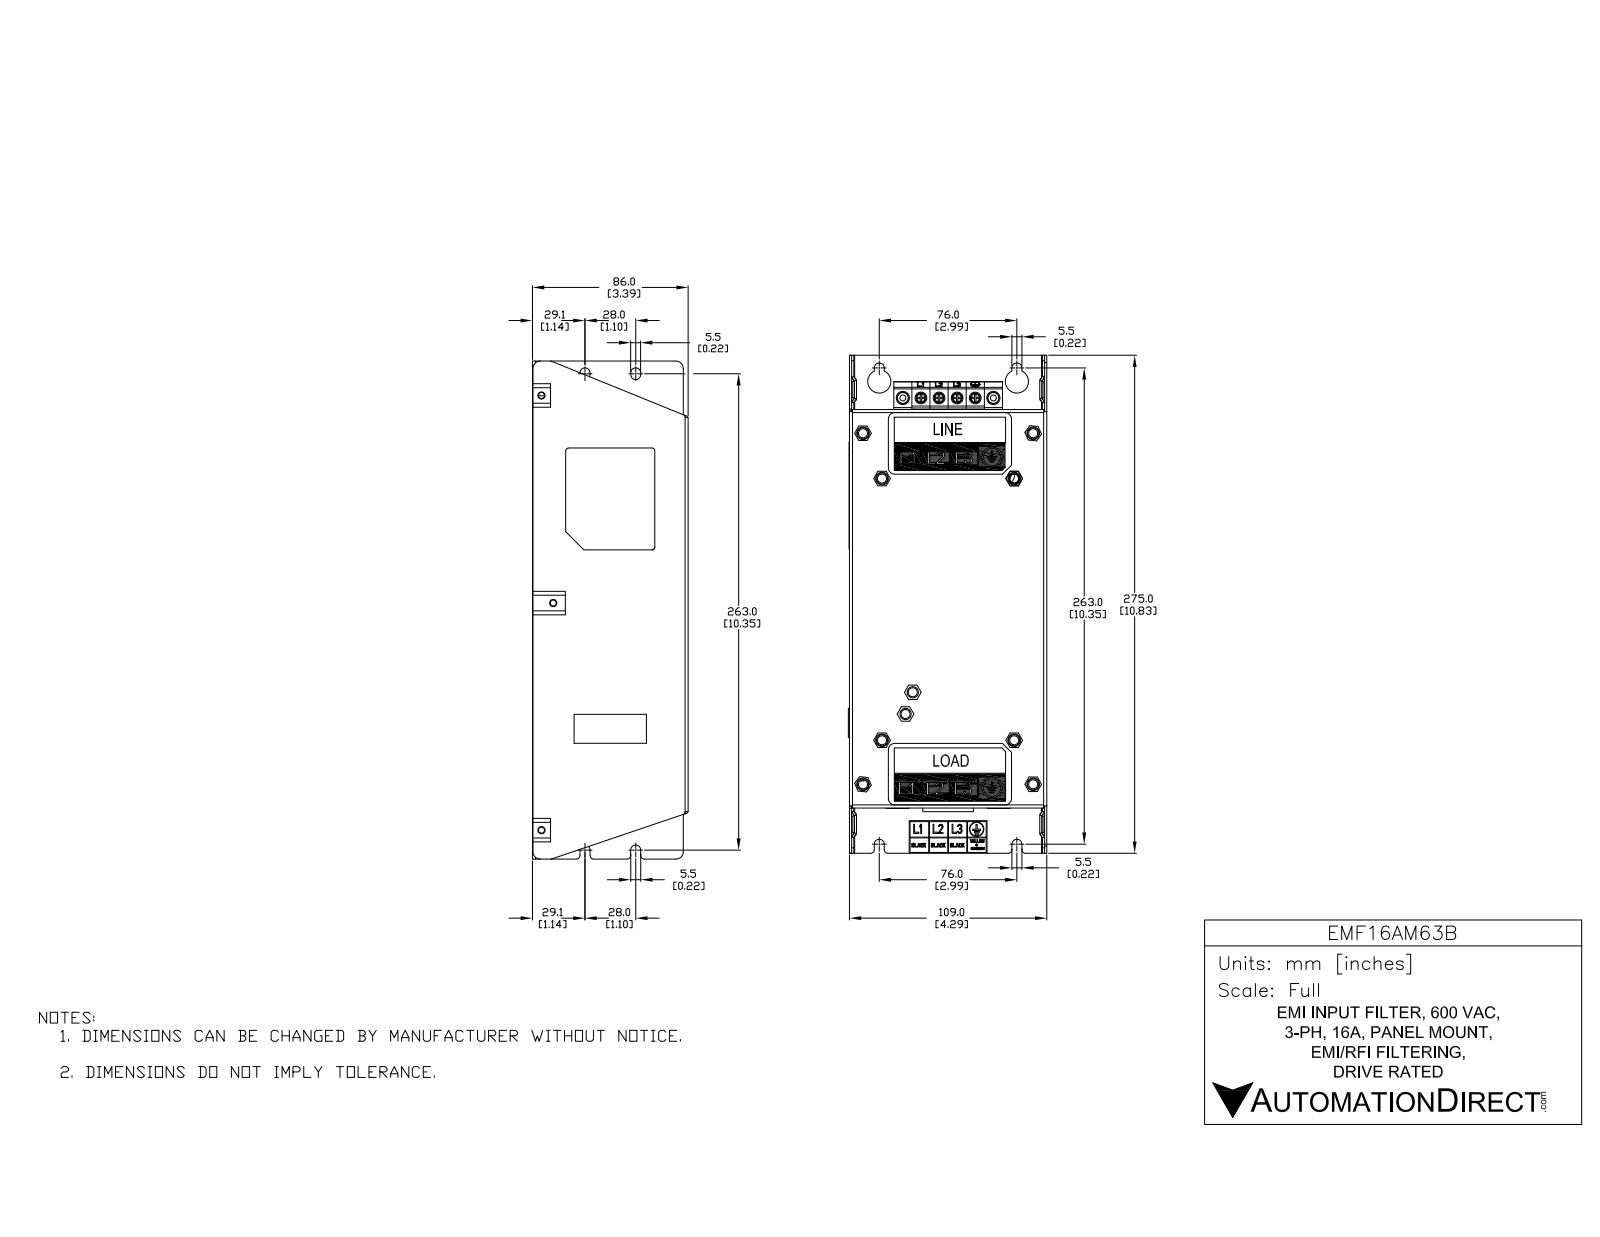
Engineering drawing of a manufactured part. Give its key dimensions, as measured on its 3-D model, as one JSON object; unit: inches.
{"part_name": "EMI B frame PRT0109 FROM wo surf 3 Coord COMPLETE E4 fXT Mod 1 r1", "step_written_by": "SolidWorks 2017 (AUTOMOTIVE_DESIGN)", "units": "inches", "bodies": {"solids": 15, "faces": 3208, "planar": 2058, "cylindrical": 618, "other": 532}, "overall_size": [10.827, 4.291, 3.39], "volume_in3": 10.93, "surface_area_in2": 435.8, "round_holes": [[0.276, 10], [0.217, 8], [0.083, 6], [0.094, 6], [0.142, 4], [0.157, 3], [0.197, 2], [0.504, 2], [0.118, 1], [0.829, 1]], "round_bosses_or_shafts": [[0.248, 8], [0.197, 8], [0.154, 8], [0.089, 6], [0.079, 6], [0.315, 4], [0.205, 2], [1.102, 1]], "partial_cylinders_radius": [[0.039, 20], [0.079, 16], [0.02, 12], [0.047, 10], [0.108, 10], [0.081, 8], [0.112, 8], [0.122, 8]], "face_to_face_distances": [0.047, 4.244, 3.323, 3.276, 3.343, 4.197, 0.067, 3.39, 4.291, 8.614], "hole_center_spacings": [0.394, 0.677, 0.551, 0.787, 0.961, 7.63, 7.983, 0.238]}
